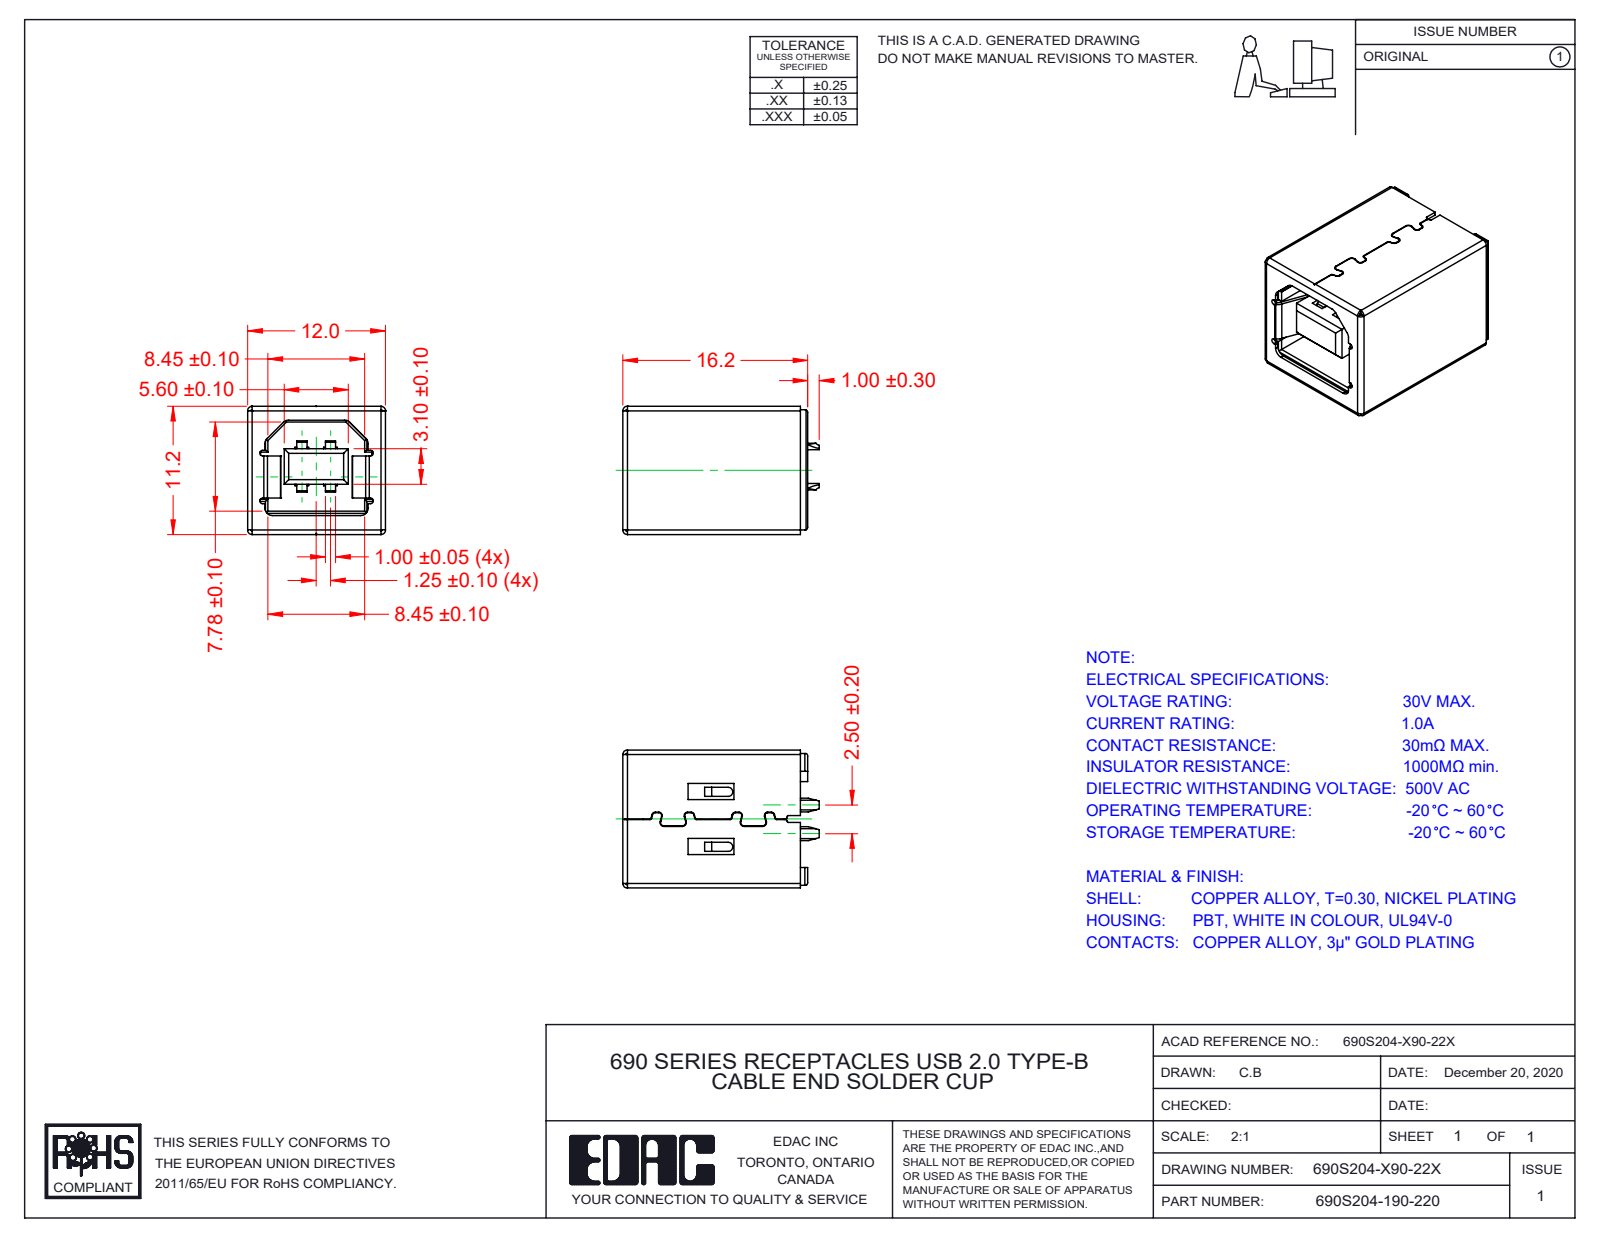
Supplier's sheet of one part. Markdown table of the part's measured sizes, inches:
| quantity | value |
| --- | --- |
| part name | Contact 690S204-X90-22X; Insulator 690S204-X90-22X_White; 690S204-190-220; Shell 690S204-X90-22X |
| STEP written by | SolidWorks 2020 (AUTOMOTIVE_DESIGN) |
| units | inches |
| bodies | 6 solids, 629 faces (428 planar, 201 cylindrical, 0 other) |
| overall size | 0.675 × 0.474 × 0.441 |
| volume | 0.083 in³ |
| surface area | 5.234 in² |
| partial cylindrical surfaces (radius × count) | 0.01 × 19, 0.012 × 14, 0.016 × 12, 0.004 × 11, 0.008 × 8, 0.014 × 8, 0.006 × 6, 0.026 × 6 |
| main face-to-face distances | 0.429, 0.462, 0.417, 0.453, 0.45, 0.465, 0.474, 0.441, 0.081, 0.016 |
